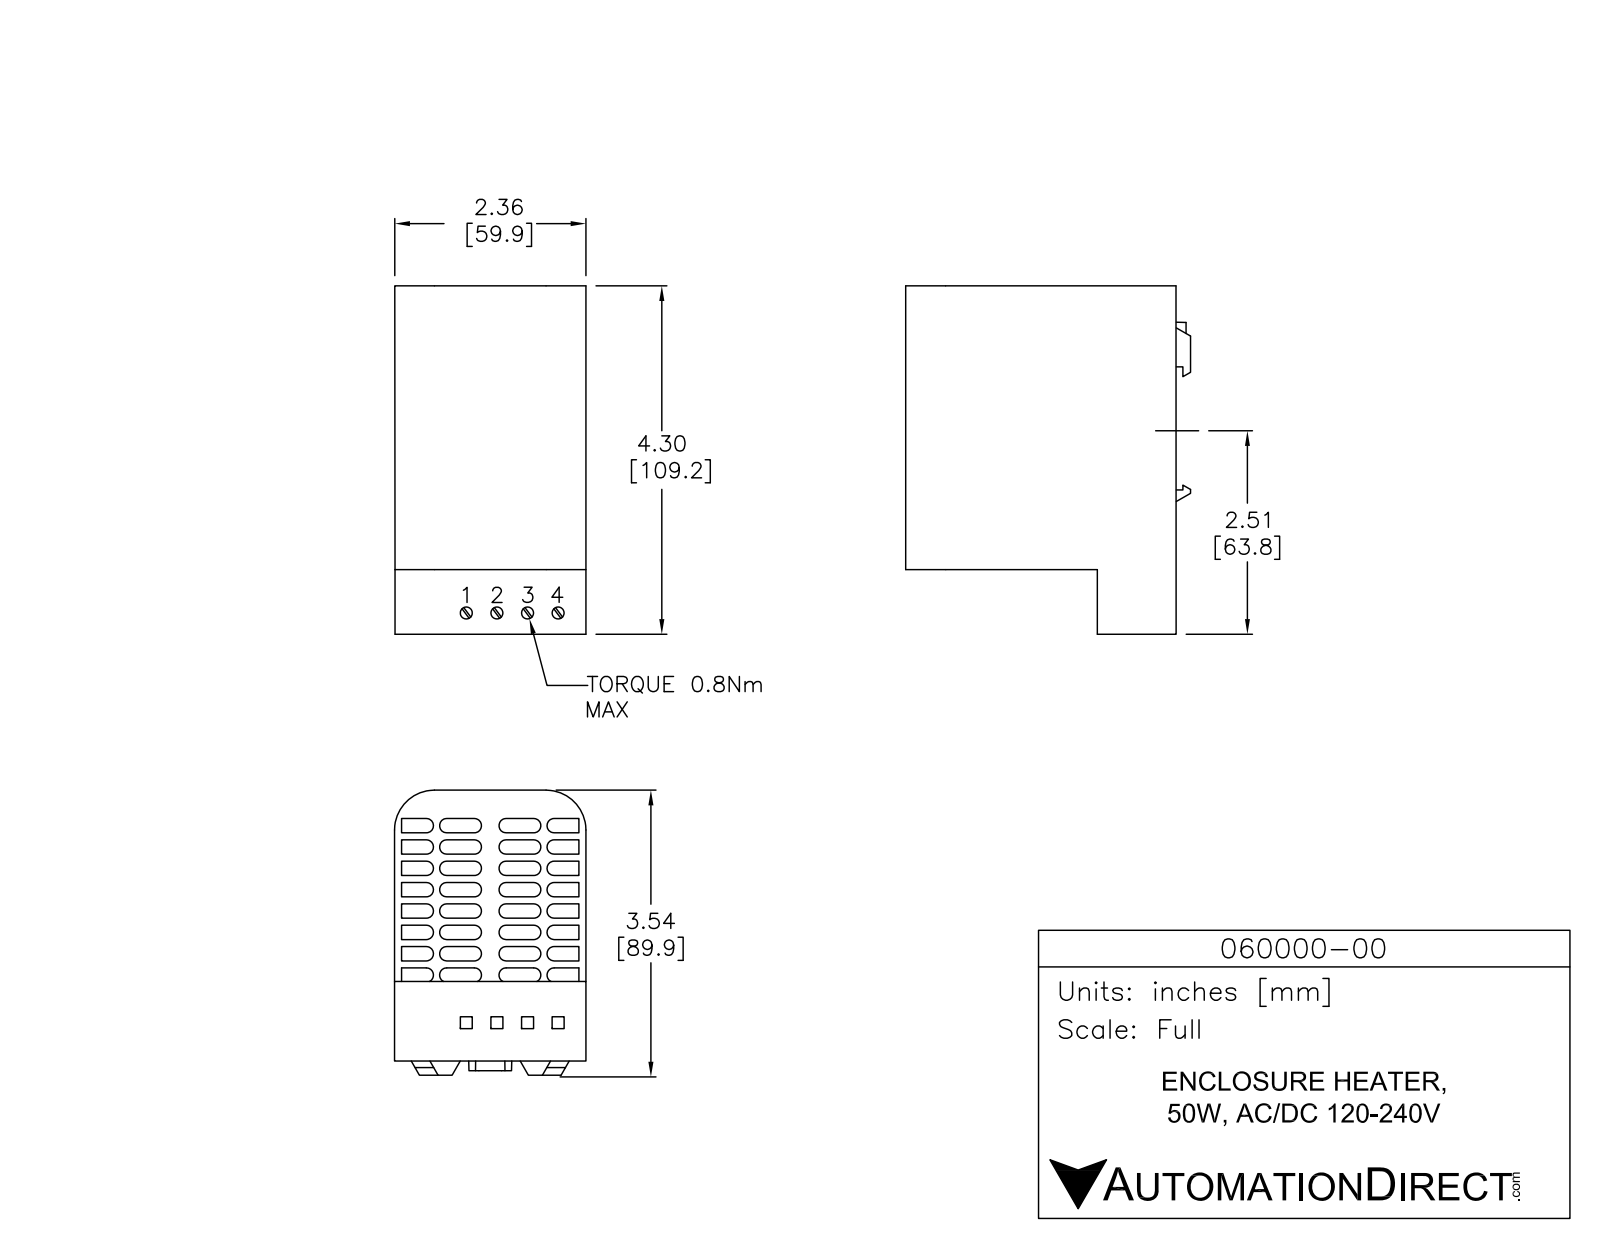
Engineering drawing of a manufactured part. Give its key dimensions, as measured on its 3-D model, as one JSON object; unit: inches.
{"part_name": "060000-00", "step_written_by": "SolidWorks 2013 (AUTOMOTIVE_DESIGN)", "units": "inches", "bodies": {"solids": 1, "faces": 817, "planar": 601, "cylindrical": 210, "other": 6}, "overall_size": [4.345, 3.58, 2.35], "volume_in3": 26.66, "surface_area_in2": 90.82, "round_holes": [[0.185, 3], [0.185, 1]], "partial_cylinders_radius": [[0.07, 88], [0.035, 18], [0.06, 6], [0.8, 2]], "face_to_face_distances": [0.03, 0.215, 0.061, 2.336, 0.2, 3.18, 2.306, 0.43, 0.03, 0.091], "hole_center_spacings": [0.4, 0.8, 1.2]}
